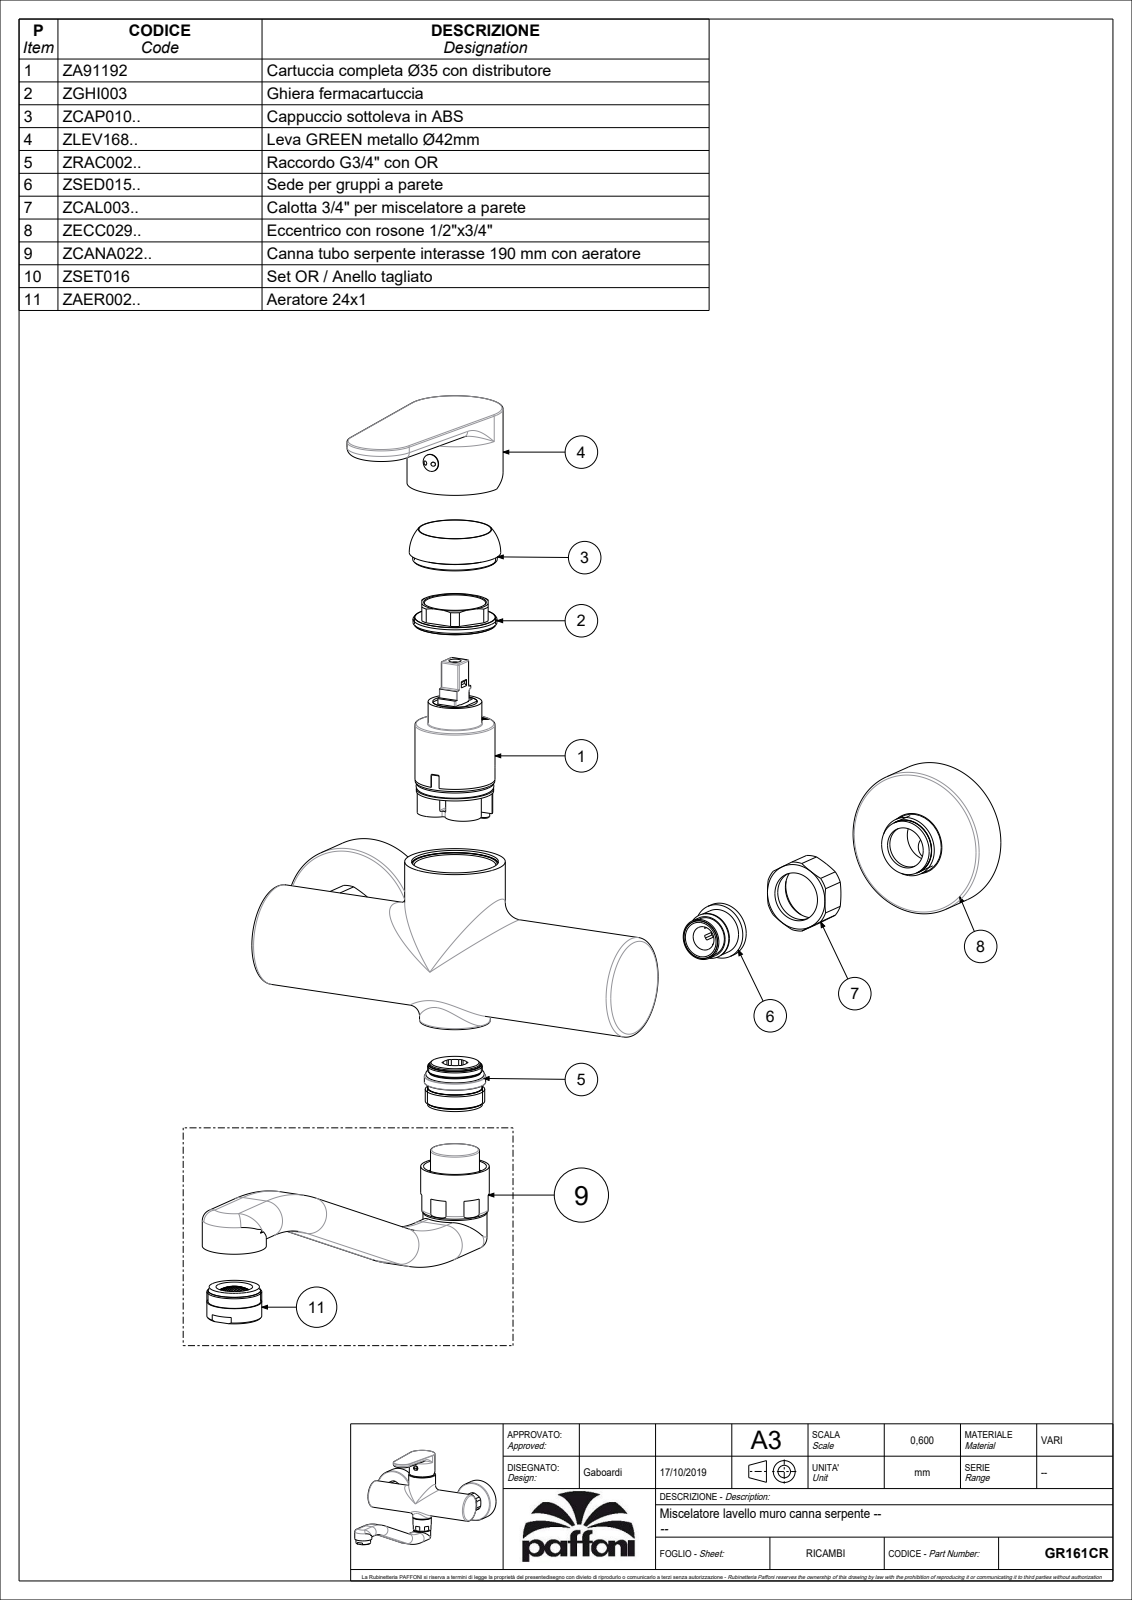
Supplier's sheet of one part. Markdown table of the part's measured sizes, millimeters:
| quantity | value |
| --- | --- |
| part name | GR161CR_SW0001 |
| STEP written by | CREO PARAMETRIC BY PTC INC, 2020044 (CONFIG_CONTROL_DESIGN) |
| units | millimeters |
| bodies | 3 solids, 510 faces (210 planar, 167 cylindrical, 133 other) |
| overall size | 264.5 × 213.5 × 146.3 |
| volume | 332 463 mm³ |
| surface area | 146 201 mm² |
| round holes (diameter × count) | 5 × 2, 7 × 2, 10.5 × 2, 16 × 2, 20.5 × 2, 36.5 × 2, 3 × 1, 4.2 × 1, 17.2 × 1, 18.2 × 1, 18.5 × 1, 20 × 1 |
| round bosses / shafts (diameter × count) | 63.5 × 2, 44 × 2, 28 × 2, 24 × 2, 19.7 × 2, 9 × 2, 42 × 1, 31 × 1 |
| partial cylindrical surfaces (radius × count) | 7.2 × 6, 8 × 6, 0.5 × 2, 3 × 2, 15.5 × 2, 94 × 2, 94.8 × 2, 109.2 × 2 |
| main face-to-face distances | 20, 0.8, 15.2, 68.5, 112.5, 83, 3.25, 177.75, 65.25, 109.25 |
| hole center spacings | 8.6, 8.63, 13.42, 13.45, 15.13, 21.93, 96.36, 188.13 |
